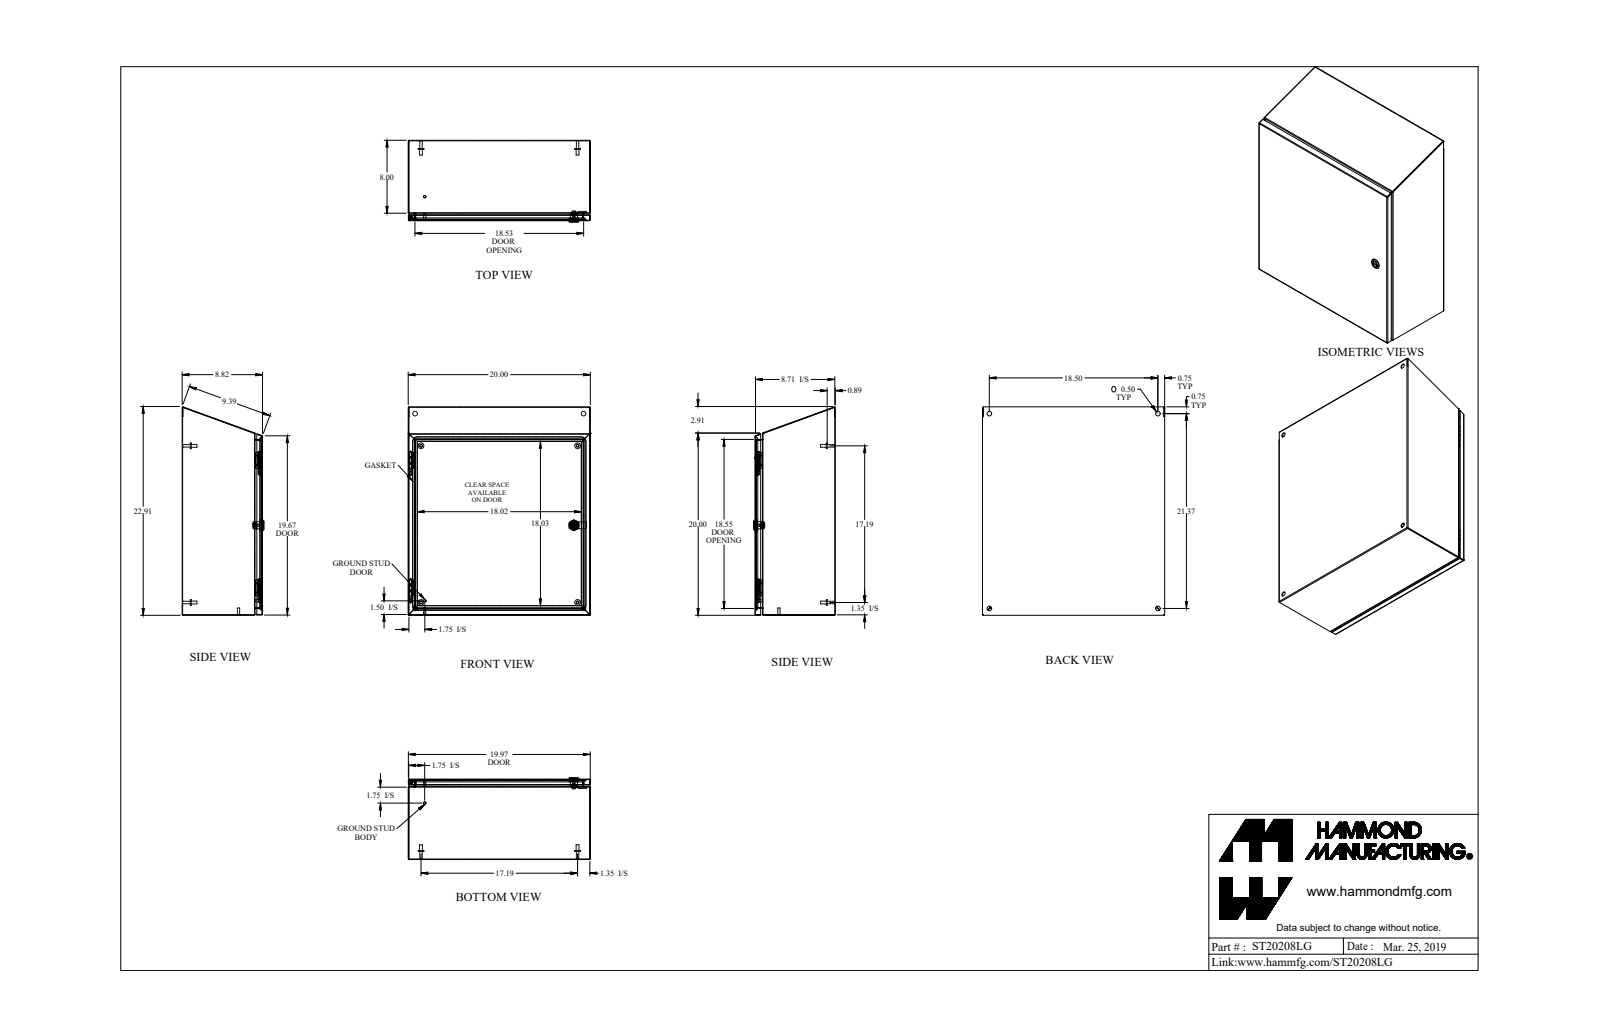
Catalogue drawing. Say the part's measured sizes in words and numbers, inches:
The part is named "ST20208LG". Its 3-D file was written by "SolidWorks 2018 (AUTOMOTIVE_DESIGN)". It is 21 solids with 632 faces: 303 planar, 197 cylindrical and 132 other. Overall it measures 22.875 by 20 by 8.982 inches. Its volume is 103.6 cubic inches and its surface area 3 538 square inches. Round holes: 4 of diameter 0.5, 1 of diameter 0.172, 1 of diameter 0.232, 1 of diameter 0.24, 1 of diameter 0.242, 1 of diameter 0.625, 1 of diameter 0.785. Round bosses or shafts: 4 of diameter 0.625, 4 of diameter 0.313, 4 of diameter 0.27, 2 of diameter 0.281, 2 of diameter 0.25, 1 of diameter 1.1, 1 of diameter 0.525, 1 of diameter 0.455. Partial cylindrical surfaces (rounded edges, fillets, slot ends): 21 of radius 0.029, 21 of radius 0.086, 11 of radius 0.25, 4 of radius 0.006, 4 of radius 0.062, 4 of radius 0.499, 2 of radius 0.125, 1 of radius 0.021. The main face-to-face distances are 0.057, 0.057, 8.765, 8.708, 8.822, 8.765, 19.943, 19.886, 20, 0.822. The hole center spacings are 18.5, 21.374, 28.269, 9.189, 12.293, 19.685, 21.311.
